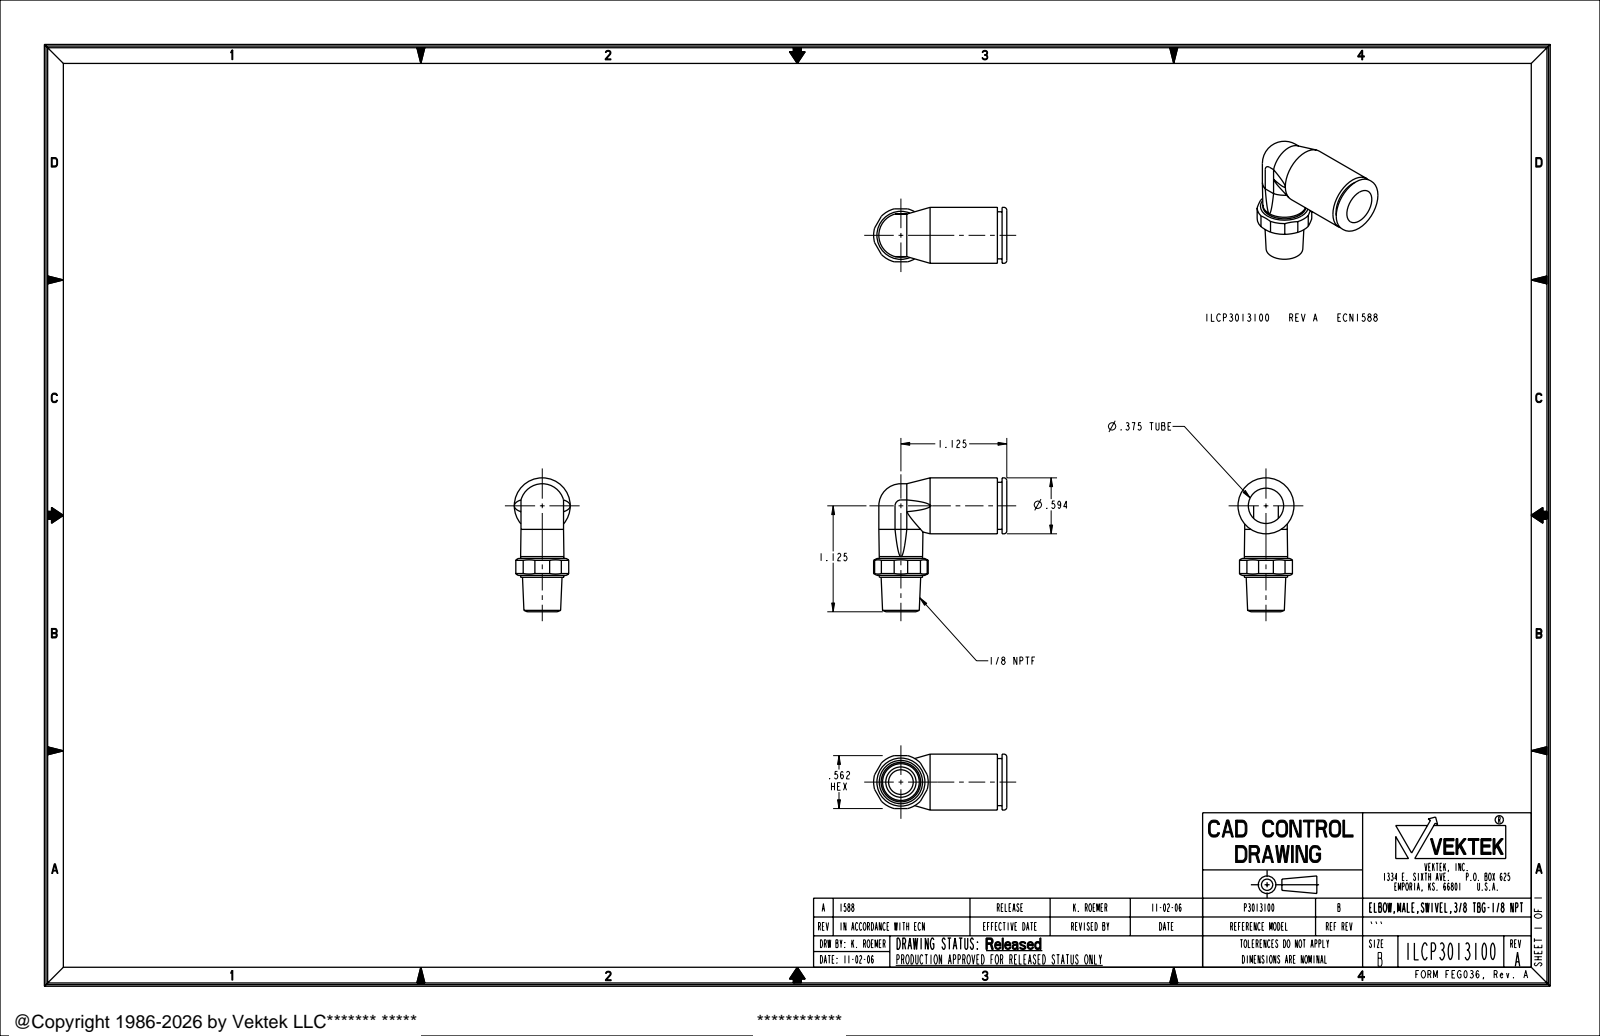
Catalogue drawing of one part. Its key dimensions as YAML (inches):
part_name: "ILCP3013100"
step_written_by: "PRO/ENGINEER BY PARAMETRIC TECHNOLOGY CORPORATION, 2005180 (AUTOMOTIVE_DESIGN_CC2)"
units: inches
bodies: {solids: 1, faces: 62, planar: 22, cylindrical: 24, other: 16}
overall_size: [1.422, 1.415, 0.594]
volume: 0.286
surface_area: 6.417
round_holes:
  - {diameter: 0.262, count: 1}
  - {diameter: 0.375, count: 1}
round_bosses_or_shafts:
  - {diameter: 0.594, count: 1}
  - {diameter: 0.5, count: 1}
  - {diameter: 0.46, count: 1}
partial_cylinders:
  - {radius: 0.234, count: 2}
  - {radius: 0.29, count: 1}
face_to_face_distances: [0.05, 0.1, 0.562, 0.055, 0.507, 0.452, 0.18, 1.125, 0.739, 0.559]
